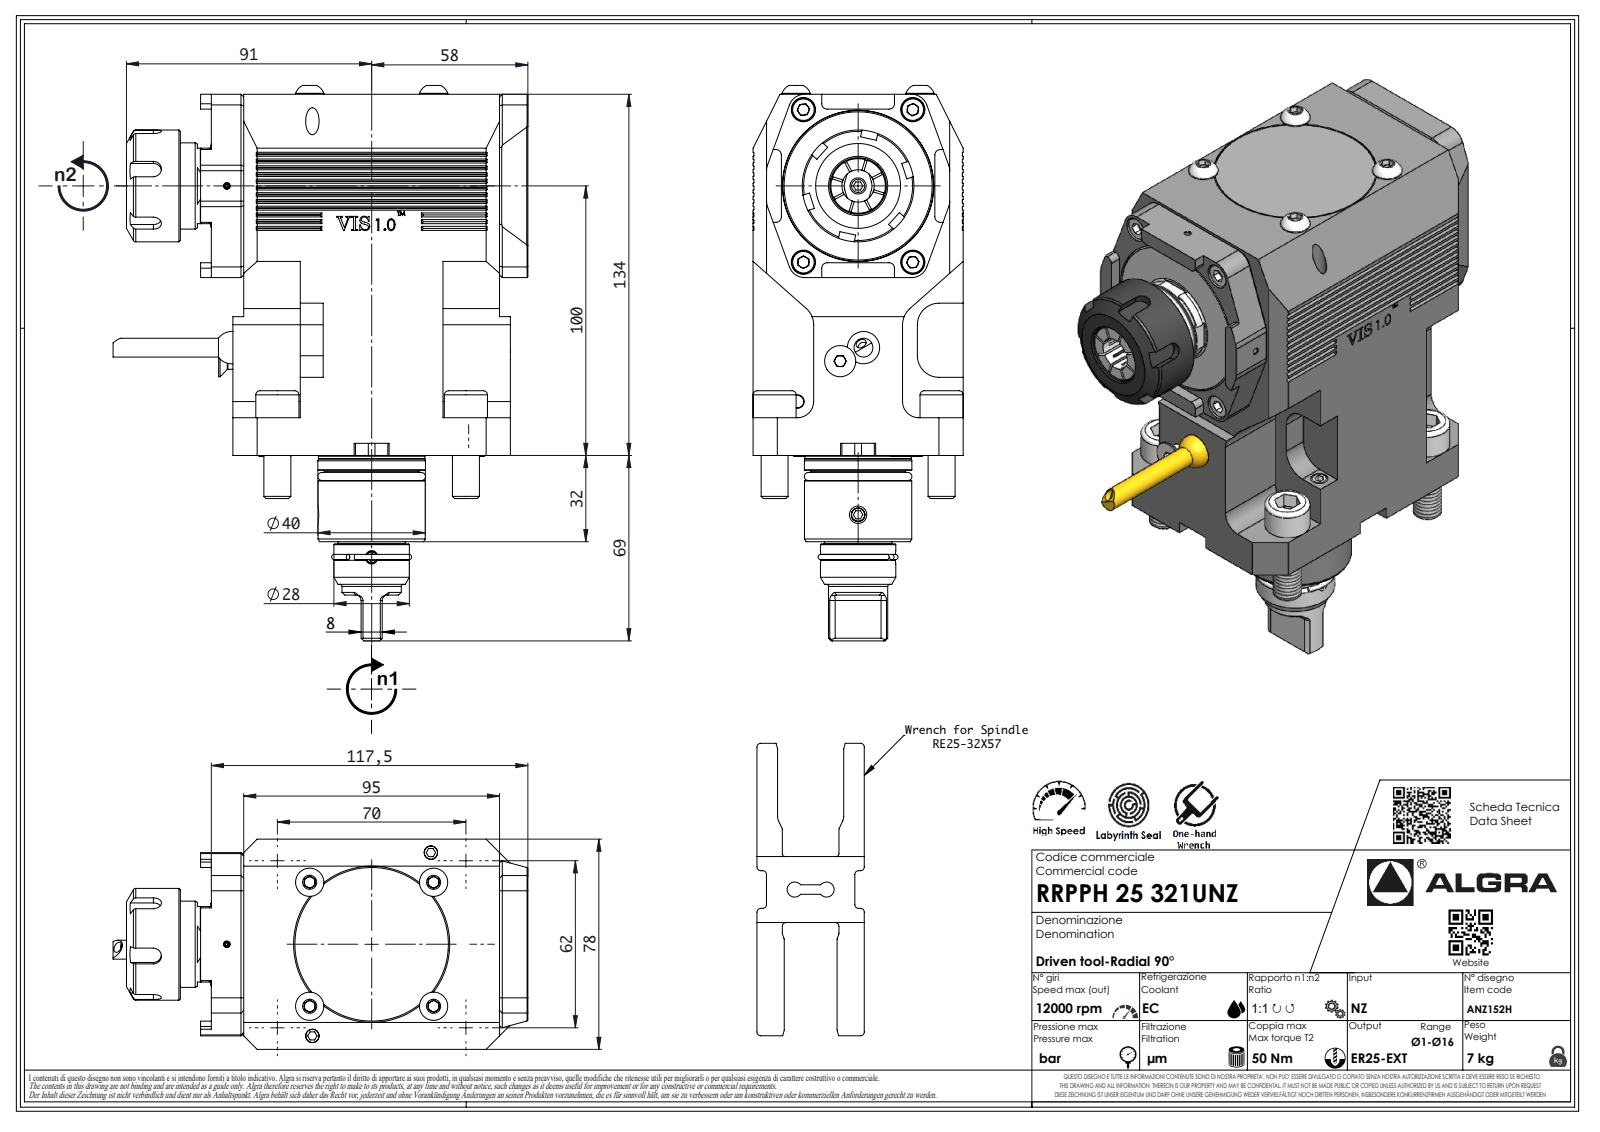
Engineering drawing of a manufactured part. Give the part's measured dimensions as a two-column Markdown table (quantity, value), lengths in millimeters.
| quantity | value |
| --- | --- |
| part name | RRPPH25321UNZ |
| STEP written by | SolidWorks 2023 (AUTOMOTIVE_DESIGN) |
| units | millimeters |
| bodies | 1 solid, 780 faces (527 planar, 127 cylindrical, 126 other) |
| overall size | 202.8 × 149.03 × 78 |
| volume | 1 071 000 mm³ |
| surface area | 87 945 mm² |
| round holes (diameter × count) | 2.1 × 1 |
| round bosses / shafts (diameter × count) | 16 × 3, 10 × 3, 41.5 × 1, 39.9 × 1, 39.8 × 1, 39.5 × 1, 35.1 × 1, 32 × 1 |
| partial cylindrical surfaces (radius × count) | 0.2 × 21, 5 × 16, 2 × 14, 6 × 10, 0.33 × 7, 0.52 × 7, 3.7 × 7, 3 × 6 |
| main face-to-face distances | 78, 134, 4, 6.5, 25, 33, 22.5, 21, 99, 74 |
